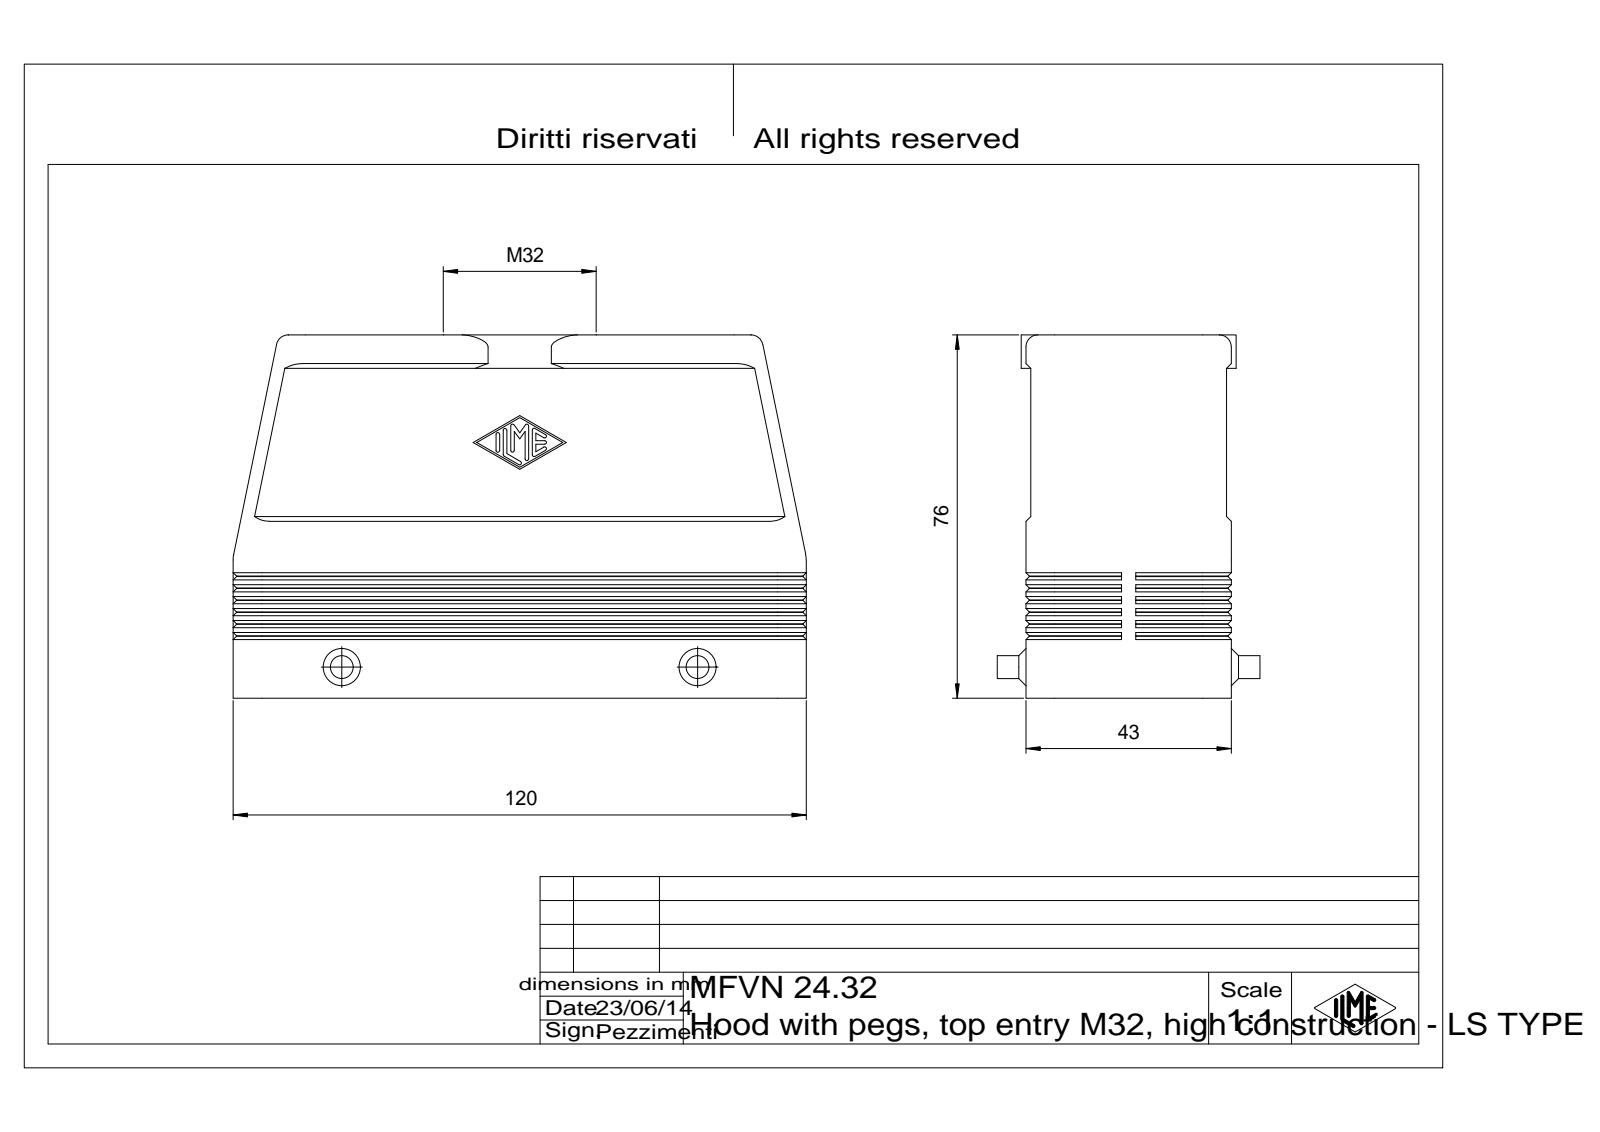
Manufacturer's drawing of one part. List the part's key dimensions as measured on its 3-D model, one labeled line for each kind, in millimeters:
Part name (STEP PRODUCT): MFVN_24.32
STEP written by: CoCreate Modeling 16.00A 16-Aug-2008 (C) Parametric Technology GmbH (AUTOMOTIVE_DESIGN)
Units: millimetres
Bodies: 1 solid, 410 faces (194 planar, 144 cylindrical, 72 other)
Overall size (bounding box): 120 × 76 × 55
Volume: 98 320 mm³ · Surface area: 52 966 mm²
Round holes (diameter × count): ⌀2.46 ×4, ⌀4 ×4, ⌀32 ×1
Round bosses / shafts (diameter × count): ⌀4.8 ×2
Partial cylindrical surfaces — rounded edges, fillets, slot ends (radius × count): R6 ×10, R2 ×4, R2.5 ×4, R3 ×4, R5.3 ×4, R22.5 ×1
Main face-to-face distances: 4, 35, 38, 3, 1, 39, 42, 41, 43, 11
Hole centre spacings: 53.72, 27, 104, 107.45
